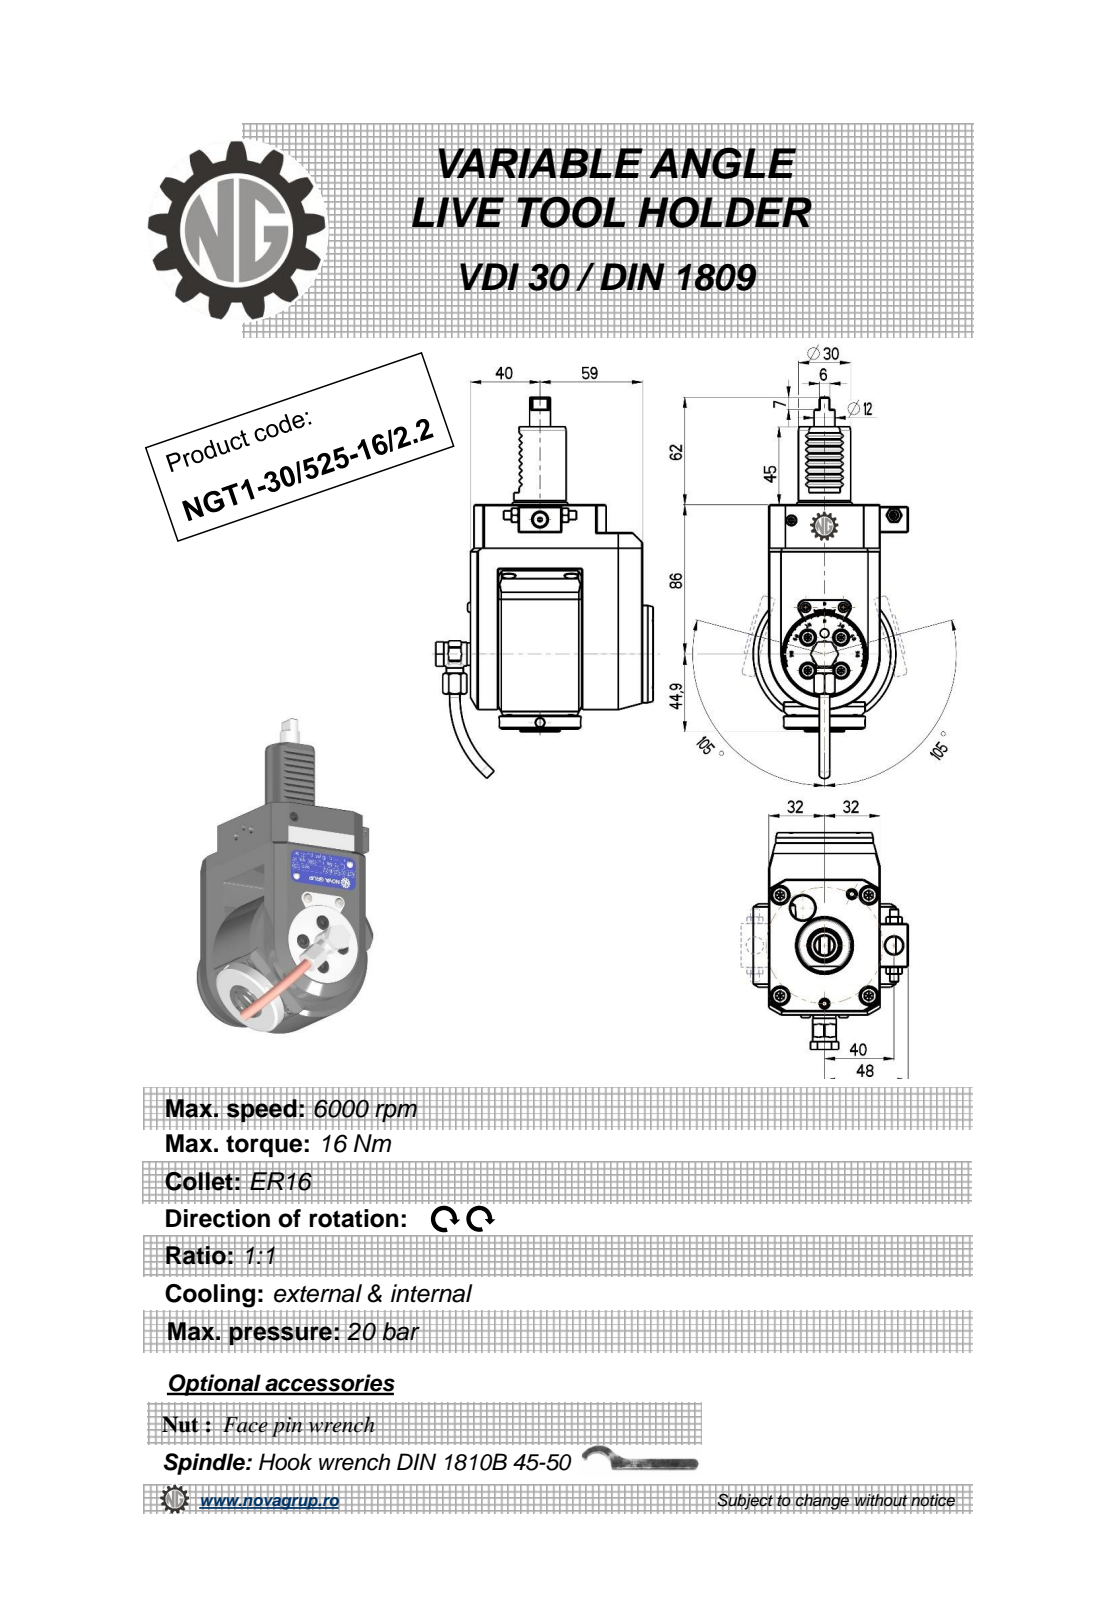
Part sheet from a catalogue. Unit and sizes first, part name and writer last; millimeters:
Units: millimetres
Overall size (bounding box): 219.67 × 124.9 × 89
Round holes (diameter × count): ⌀3.2 ×4, ⌀4 ×3, ⌀5 ×2, ⌀10 ×2, ⌀3 ×1, ⌀4.2 ×1, ⌀6.2 ×1, ⌀9 ×1, ⌀9.5 ×1, ⌀11 ×1, ⌀12.5 ×1
Round bosses / shafts (diameter × count): ⌀6 ×2, ⌀5.7 ×2, ⌀56 ×1, ⌀47 ×1, ⌀35 ×1, ⌀30 ×1, ⌀23 ×1, ⌀13.6 ×1
Partial cylindrical surfaces — rounded edges, fillets, slot ends (radius × count): R0.26 ×12, R0.3 ×8, R0.16 ×6, R0.5 ×6, R1 ×2, R7.7 ×1, R32 ×1, R41 ×1
Main face-to-face distances: 64, 16, 37, 99, 6, 105, 21, 14, 62, 35
Hole centre spacings: 9.25, 13.08, 18.5, 41.06, 49.87, 50.26, 0.4, 30.75
Volume: 770 185 mm³ · Surface area: 70 510 mm²
Bodies: 1 solid, 489 faces (208 planar, 134 cylindrical, 147 other)
Part name (STEP PRODUCT): NGT1_30_521_16_2_2
STEP written by: PRO/ENGINEER BY PARAMETRIC TECHNOLOGY CORPORATION, 2010280 (CONFIG_CONTROL_DESIGN)
